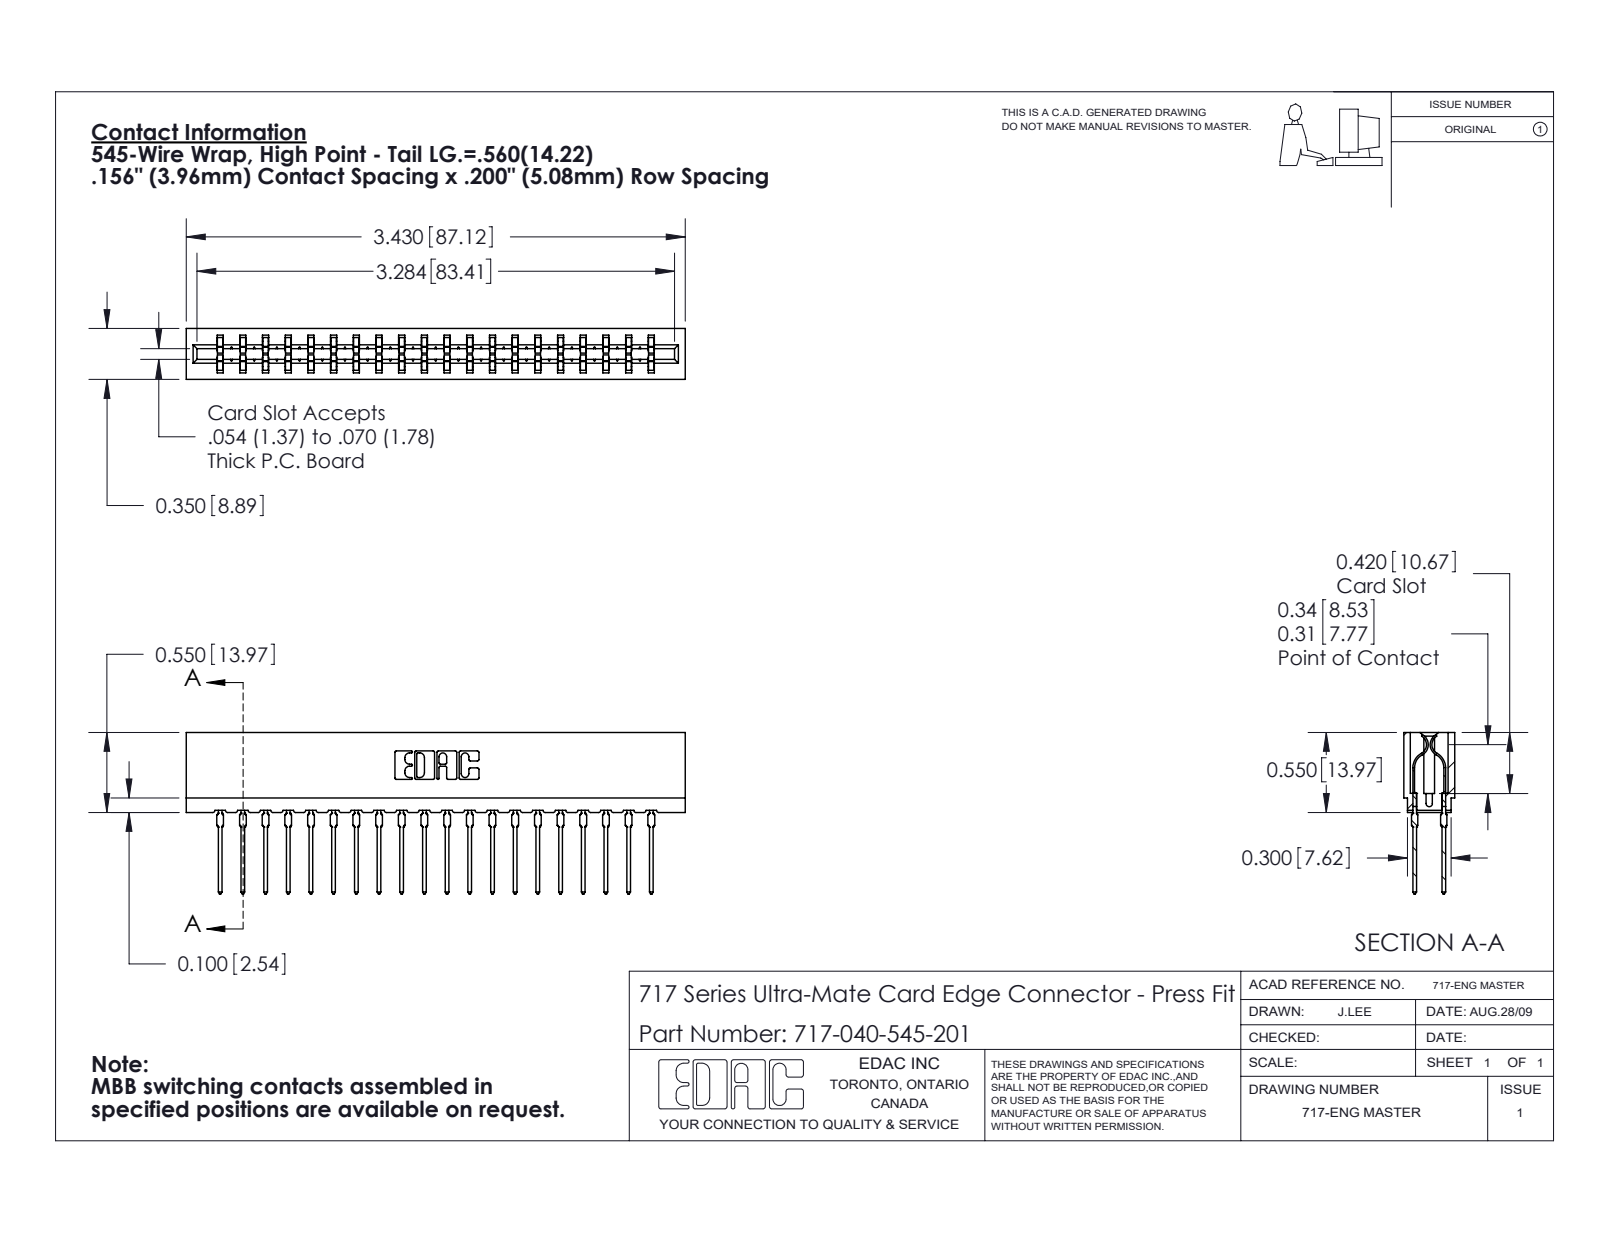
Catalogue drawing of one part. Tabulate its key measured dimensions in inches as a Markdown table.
| quantity | value |
| --- | --- |
| part name | 717-040-545-201; 717 Part_Insulator Option - 06; 745-292-001_545 |
| STEP written by | SolidWorks 2020 (CONFIG_CONTROL_DESIGN) |
| units | inches |
| bodies | 41 solids, 3694 faces (1914 planar, 740 cylindrical, 1040 other) |
| overall size | 3.43 × 1.109 × 0.35 |
| volume | 0.475 in³ |
| surface area | 19.04 in² |
| partial cylindrical surfaces (radius × count) | 0.021 × 80, 0.015 × 40, 0.01 × 22, 0.005 × 8, 0.011 × 8, 0.007 × 6, 0.031 × 6, 0.026 × 3 |
| main face-to-face distances | 0.212, 0.138, 0.35, 0.063, 0.287, 0.076, 0.149, 0.156, 0.074, 0.624 |
